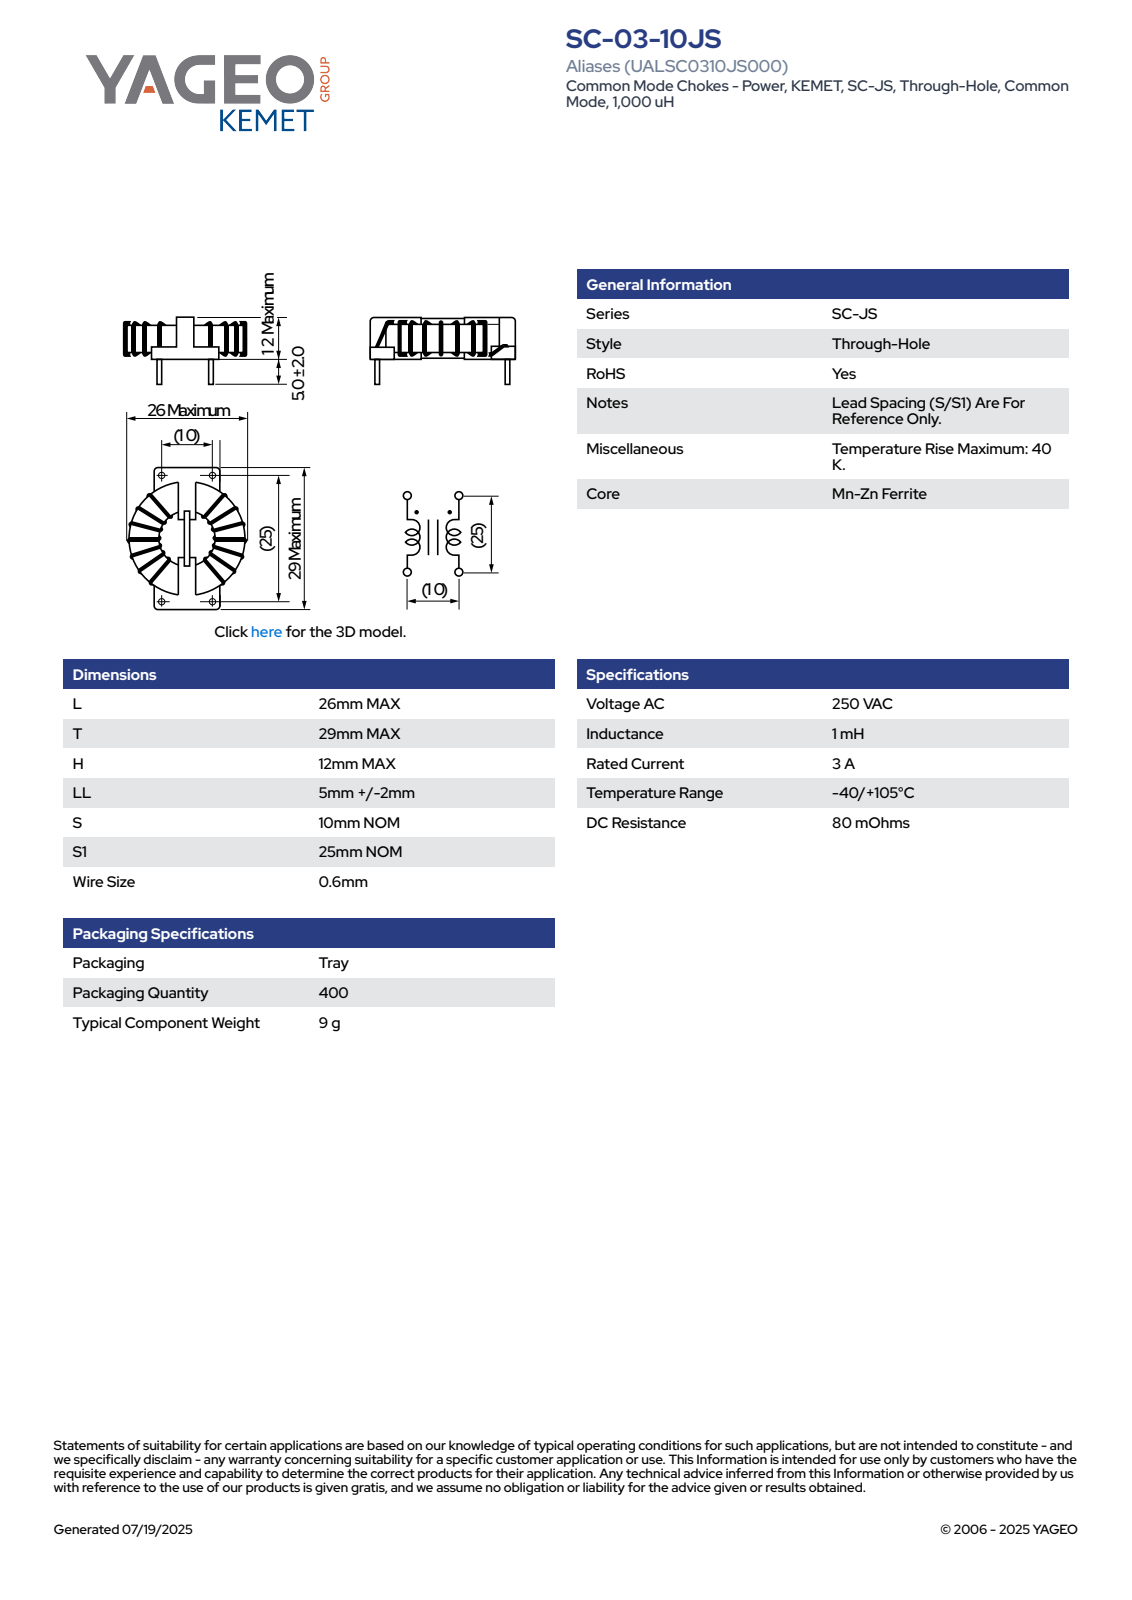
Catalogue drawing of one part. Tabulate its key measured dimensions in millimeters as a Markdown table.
| quantity | value |
| --- | --- |
| part name | SC-03-10JS |
| STEP written by | SolidWorks 2018 (AUTOMOTIVE_DESIGN) |
| units | millimeters |
| bodies | 1 solid, 337 faces (140 planar, 125 cylindrical, 72 other) |
| overall size | 29 × 26 × 15.49 |
| volume | 4 037 mm³ |
| surface area | 3 227 mm² |
| round holes (diameter × count) | 0.7 × 4, 1.6 × 2 |
| round bosses / shafts (diameter × count) | 0.6 × 10, 1.5 × 2 |
| partial cylindrical surfaces (radius × count) | 0.3 × 16, 0.2 × 14, 1.5 × 4, 0.7 × 2, 4 × 1, 4.97 × 1, 5.38 × 1, 5.47 × 1 |
| main face-to-face distances | 2.15, 1.05, 8.62, 1.4, 10.02, 1.1, 3.2, 4.15, 4.04, 0.8 |
| hole center spacings | 5, 25.5, 25, 10, 26.93 |
